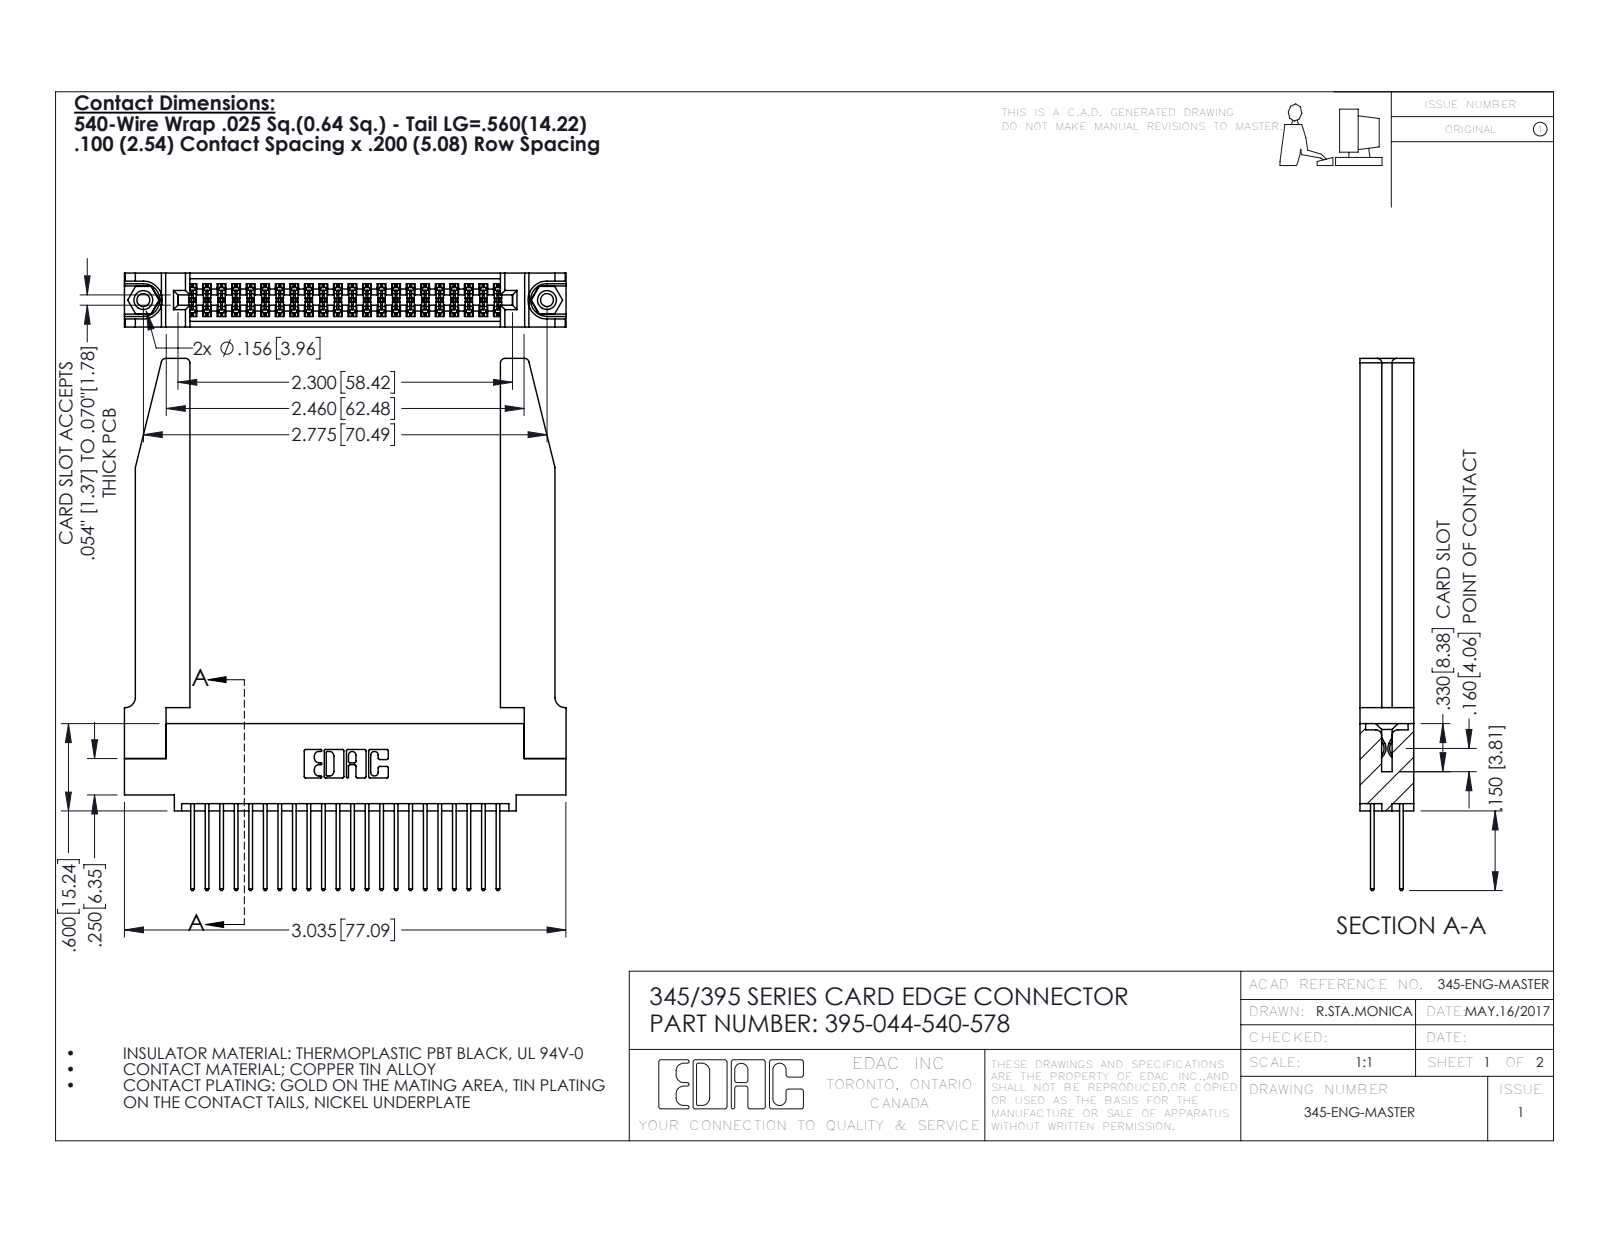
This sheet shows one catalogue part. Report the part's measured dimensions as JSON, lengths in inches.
{"part_name": "345 Part_0.110 Offset - 0.156 Dia-TH; 345-220-078_345-220-078; 345-250-001_345-250-001-102; 345-292-001_345-293-140 (+1 more)", "step_written_by": "SolidWorks 2016 (CONFIG_CONTROL_DESIGN)", "units": "inches", "bodies": {"solids": 49, "faces": 2564, "planar": 1678, "cylindrical": 834, "other": 52}, "overall_size": [3.657, 3.036, 0.37], "volume_in3": 0.926, "surface_area_in2": 28.29, "round_holes": [[0.089, 2], [0.125, 2], [0.156, 2], [0.064, 1]], "round_bosses_or_shafts": [[0.155, 2]], "partial_cylinders_radius": [[0.006, 66], [0.01, 44], [0.01, 22], [0.03, 8], [0.007, 6], [0.031, 6], [0.026, 3], [0.014, 2]], "face_to_face_distances": [0.37, 0.072, 0.298, 0.2, 0.098, 0.272, 0.025, 0.225, 0.148, 0.15], "hole_center_spacings": [0.27, 2.541, 2.775]}
